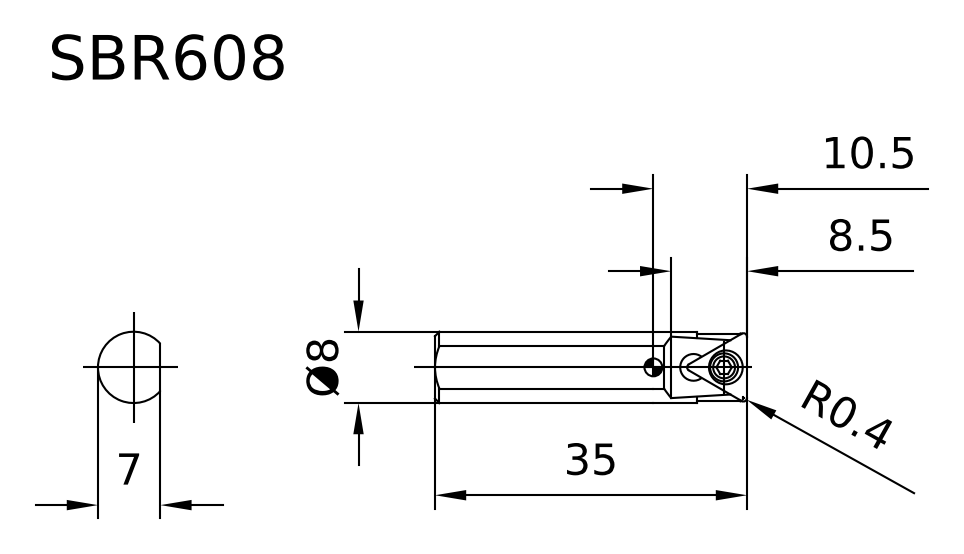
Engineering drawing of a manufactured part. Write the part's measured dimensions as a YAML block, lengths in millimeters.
part_name: "SBR608_ASM"
step_written_by: "SIEMENS PLM Software NX 10.0 (AUTOMOTIVE_DESIGN)"
units: millimeters
bodies: {solids: 2, faces: 64, planar: 20, cylindrical: 28, other: 16}
overall_size: [34.65, 8, 7.37]
volume: 1503
surface_area: 1020
round_holes:
  - {diameter: 1, count: 1}
  - {diameter: 2, count: 1}
round_bosses_or_shafts:
  - {diameter: 3.2, count: 1}
partial_cylinders:
  - {radius: 0.16, count: 6}
  - {radius: 0.36, count: 6}
  - {radius: 0.1, count: 4}
  - {radius: 0.5, count: 1}
  - {radius: 1, count: 1}
  - {radius: 3.8, count: 1}
  - {radius: 4, count: 1}
face_to_face_distances: [2.08, 29.05, 2.13, 4.21, 2, 4.99, 2.86, 0.78, 5.6, 34.65]
